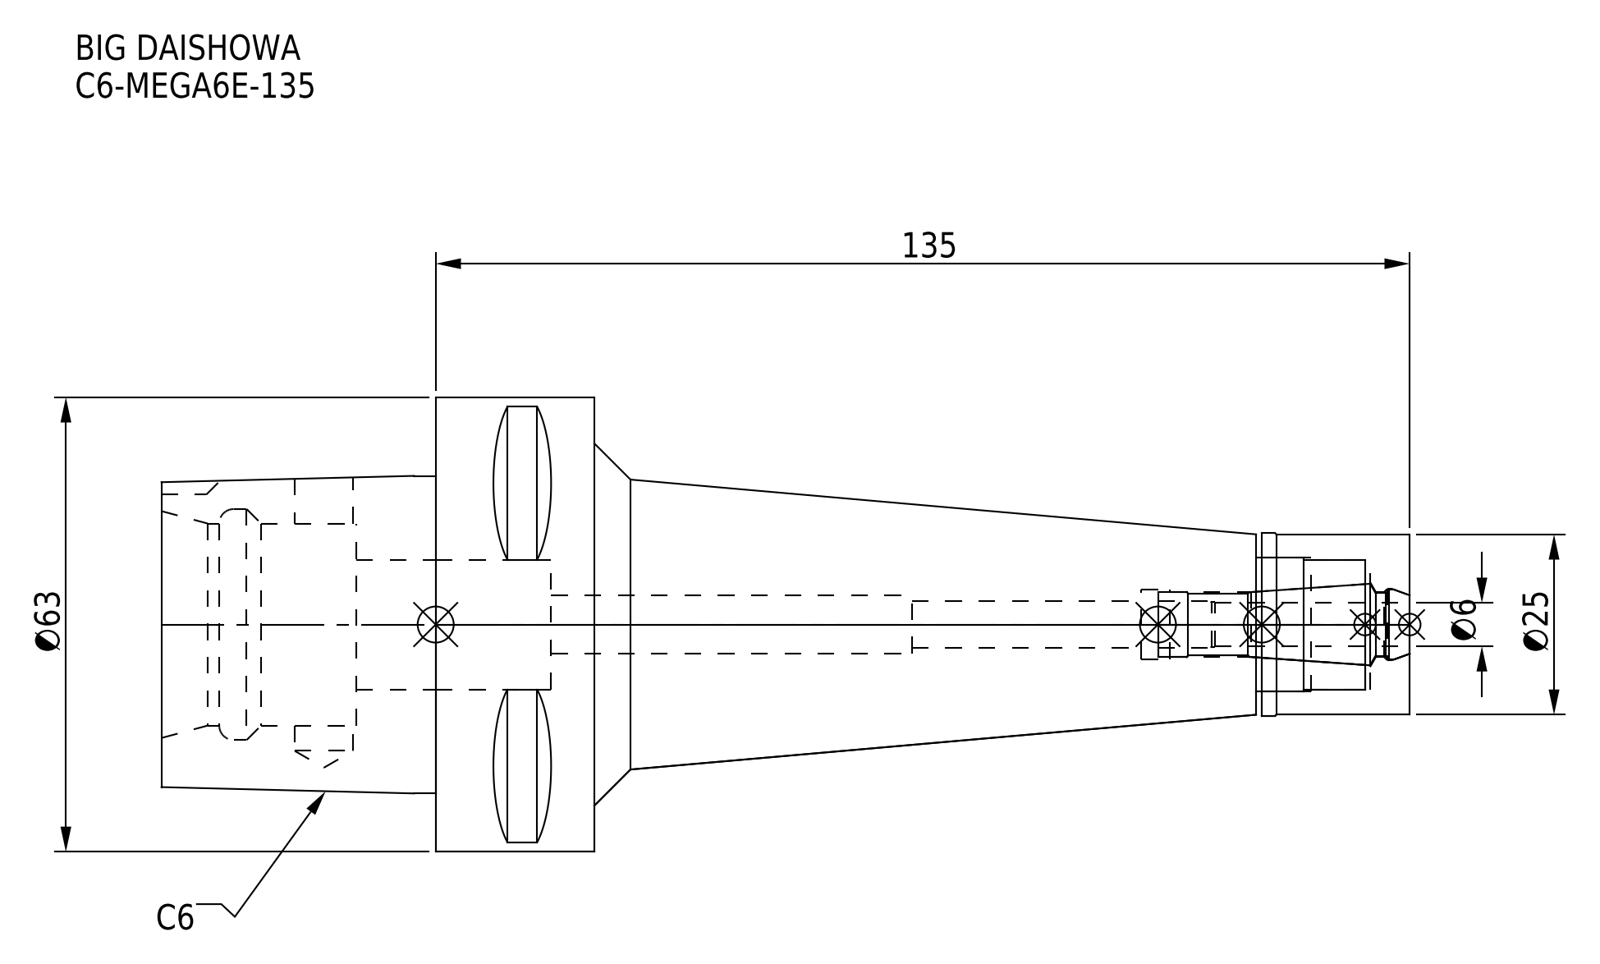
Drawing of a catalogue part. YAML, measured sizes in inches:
part_name: "C6-MEGA6E-135-060_ASM.stp; C6-MEGA6E-135; DXF_TEMP_ASSY_ASM_4_ASM.stp; C6-MEGA6E-135_1.stp (+3 more)"
step_written_by: "SolidWorks 2019 (CONFIG_CONTROL_DESIGN)"
units: inches
bodies: {solids: 2, faces: 100, planar: 37, cylindrical: 39, other: 24}
overall_size: [6.811, 2.48, 2.48]
volume: 11.12
surface_area: 55.32
round_holes:
  - {diameter: 0.252, count: 1}
  - {diameter: 0.315, count: 1}
  - {diameter: 0.319, count: 1}
  - {diameter: 0.354, count: 1}
  - {diameter: 0.378, count: 1}
  - {diameter: 0.39, count: 1}
  - {diameter: 0.709, count: 1}
  - {diameter: 0.728, count: 1}
  - {diameter: 1.102, count: 1}
  - {diameter: 1.26, count: 1}
round_bosses_or_shafts:
  - {diameter: 2.48, count: 1}
  - {diameter: 0.996, count: 1}
  - {diameter: 0.984, count: 1}
partial_cylinders:
  - {radius: 0.197, count: 1}
face_to_face_distances: [0.866, 1.063, 2.362, 1.496, 4.449, 5.315, 6.811, 5.748, 1.299, 0.433]
